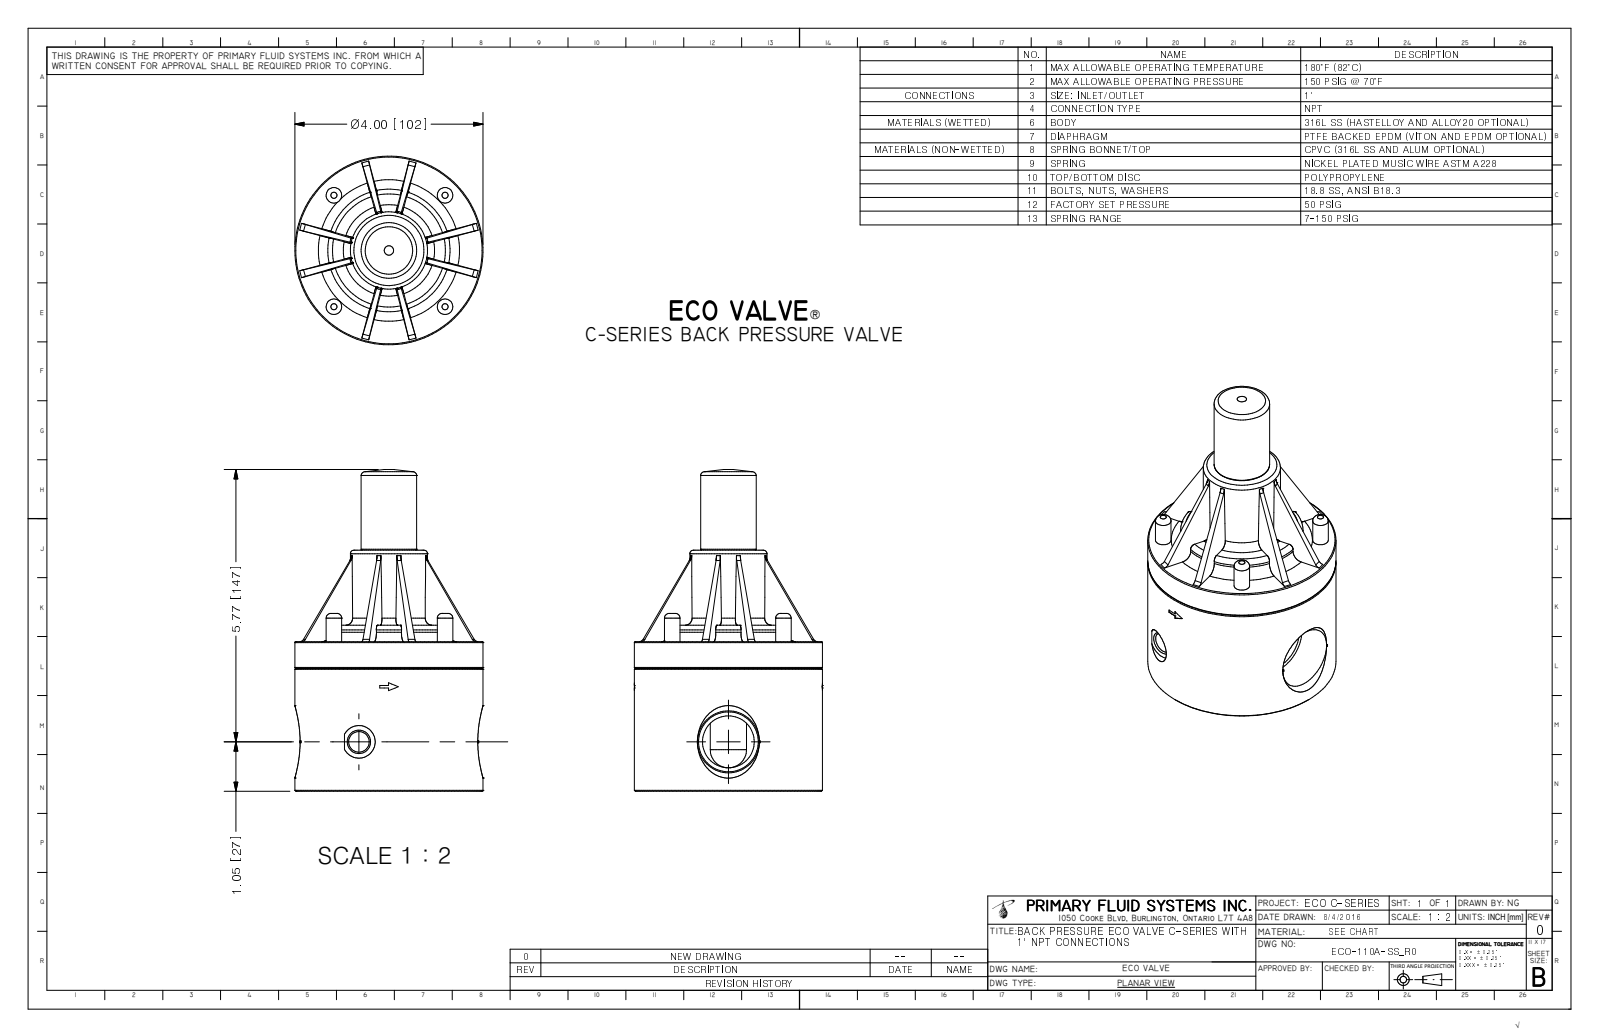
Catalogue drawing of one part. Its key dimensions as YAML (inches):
part_name: "ECO-110A-SS_R0"
step_written_by: "Autodesk Inventor 2009 (AUTOMOTIVE_DESIGN)"
units: inches
bodies: {solids: 1, faces: 221, planar: 103, cylindrical: 52, other: 66}
overall_size: [6.824, 4, 4]
volume: 45.46
surface_area: 116.1
round_holes:
  - {diameter: 0.23, count: 4}
  - {diameter: 0.4, count: 4}
  - {diameter: 0.257, count: 1}
  - {diameter: 0.438, count: 1}
  - {diameter: 0.691, count: 1}
round_bosses_or_shafts:
  - {diameter: 0.33, count: 4}
  - {diameter: 0.256, count: 4}
  - {diameter: 4, count: 1}
  - {diameter: 2.6, count: 1}
  - {diameter: 1.64, count: 1}
  - {diameter: 1.18, count: 1}
partial_cylinders:
  - {radius: 0.1, count: 8}
  - {radius: 0.128, count: 4}
  - {radius: 0.129, count: 3}
  - {radius: 0.2, count: 3}
  - {radius: 1.999, count: 1}
face_to_face_distances: [3.174, 3.524, 0.35, 2.338, 5.114, 1.94, 1.59, 0.27, 0.275, 2.899]
hole_center_spacings: [2.363, 2.363, 2.386, 2.386, 0.023, 3.342, 3.358, 3.374]
